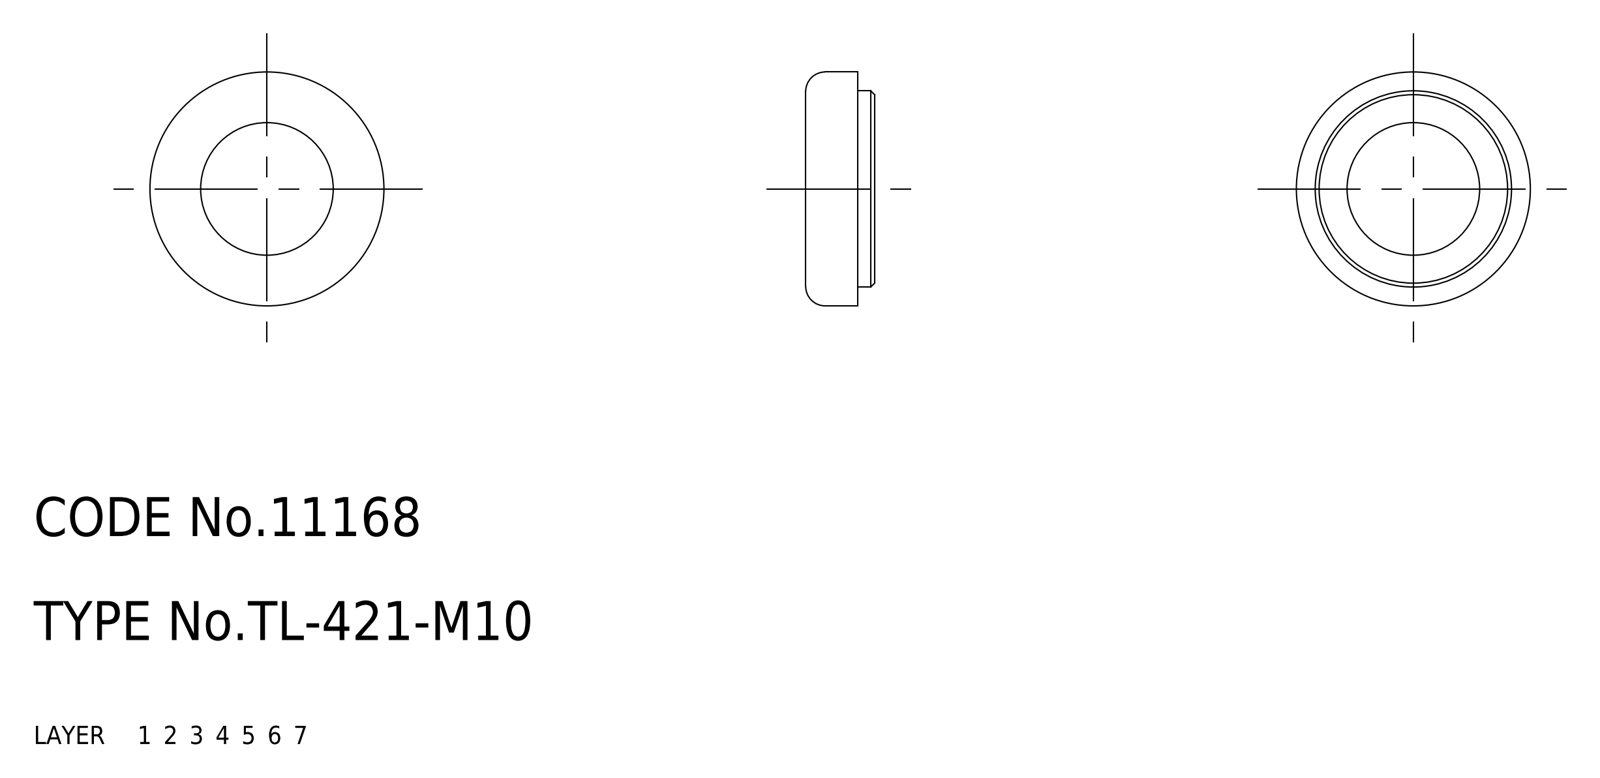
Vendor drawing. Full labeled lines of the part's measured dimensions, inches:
Part name (STEP PRODUCT): washer; packing; TL_421_M10
STEP written by: SolidWorks 2015 (AUTOMOTIVE_DESIGN)
Units: inches
Bodies: 2 solids, 22 faces (6 planar, 12 cylindrical, 4 other)
Overall size (bounding box): 0.709 × 0.709 × 0.209
Volume: 0.048 in³ · Surface area: 1.841 in²
Round holes (diameter × count): ⌀0.402 ×1, ⌀0.591 ×1
Round bosses / shafts (diameter × count): ⌀0.709 ×1, ⌀0.594 ×1
Main face-to-face distances: 0.059, 0.209, 0.15, 0.157, 0.098, 0.051
